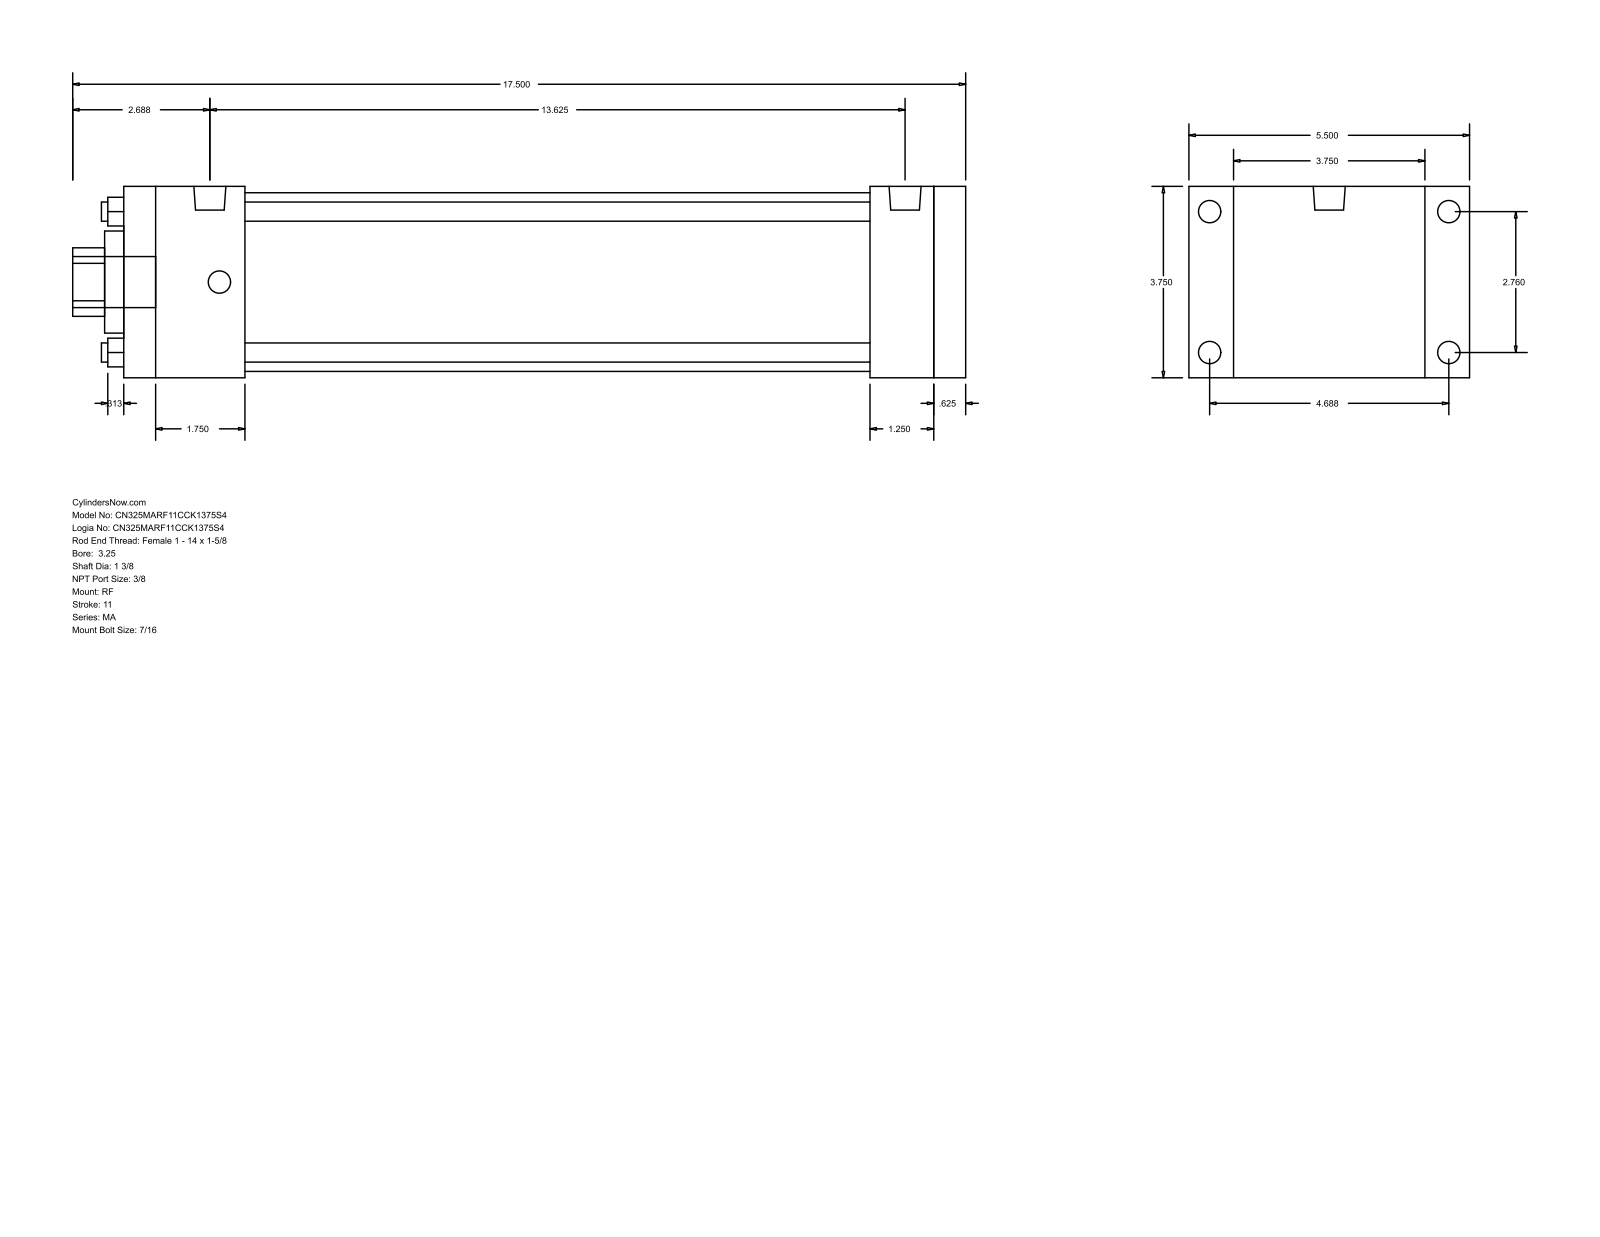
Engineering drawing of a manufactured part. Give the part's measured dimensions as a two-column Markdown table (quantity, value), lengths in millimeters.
| quantity | value |
| --- | --- |
| part name | MA_RF__0325_1.375 |
| STEP written by | GSSL Pune (CONFIG_CONTROL_DESIGN) |
| units | millimeters |
| bodies | 0 solids, 92 faces (64 planar, 28 cylindrical, 0 other) |
| overall size | 444.5 × 139.7 × 95.25 |
| round holes (diameter × count) | 9.53 × 4, 34.92 × 1, 50.8 × 1, 88.9 × 1 |
| round bosses / shafts (diameter × count) | 11.11 × 8, 15.93 × 2, 25.4 × 1 |
| partial cylindrical surfaces (radius × count) | 17.06 × 1 |
| main face-to-face distances | 95.24, 419.1, 15.88, 403.22, 22.23, 117.47, 371.48, 31.74, 47.62, 60.32 |
| hole center spacings | 49.57, 70.1, 99.14 |
